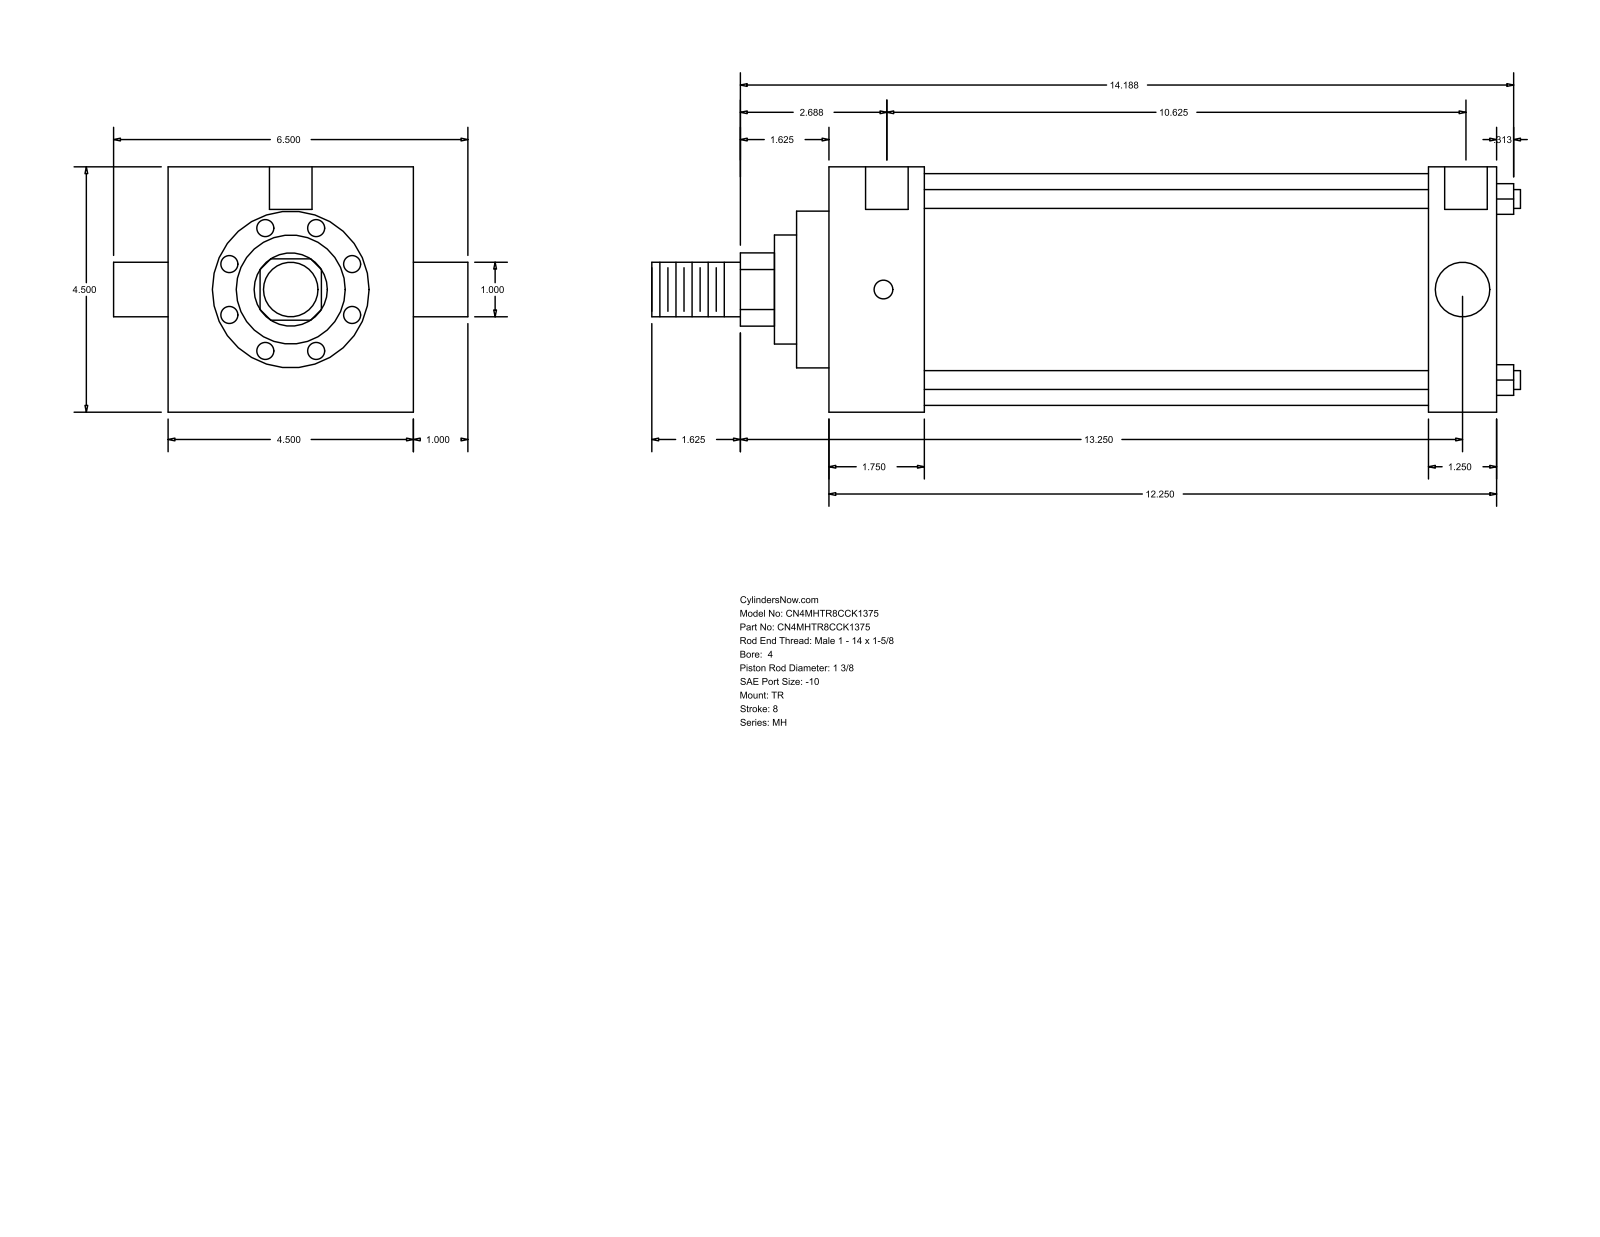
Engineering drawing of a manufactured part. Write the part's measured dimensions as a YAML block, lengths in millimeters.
part_name: "MH_TR__0400_1.375"
step_written_by: "GSSL Pune (CONFIG_CONTROL_DESIGN)"
units: millimeters
bodies: {solids: 0, faces: 86, planar: 61, cylindrical: 25, other: 0}
overall_size: [404.81, 165.1, 114.3]
round_holes:
  - {diameter: 8.73, count: 3}
  - {diameter: 19.84, count: 2}
round_bosses_or_shafts:
  - {diameter: 8.76, count: 4}
  - {diameter: 25.4, count: 2}
  - {diameter: 107.95, count: 1}
  - {diameter: 73.03, count: 1}
  - {diameter: 50.8, count: 1}
  - {diameter: 34.92, count: 1}
partial_cylinders:
  - {radius: 17.06, count: 1}
face_to_face_distances: [114.3, 311.16, 44.45, 266.71, 279.41, 234.96, 31.75, 15.08, 59.53, 294.49]
hole_center_spacings: [1.59, 271.47, 269.88, 273.06]
